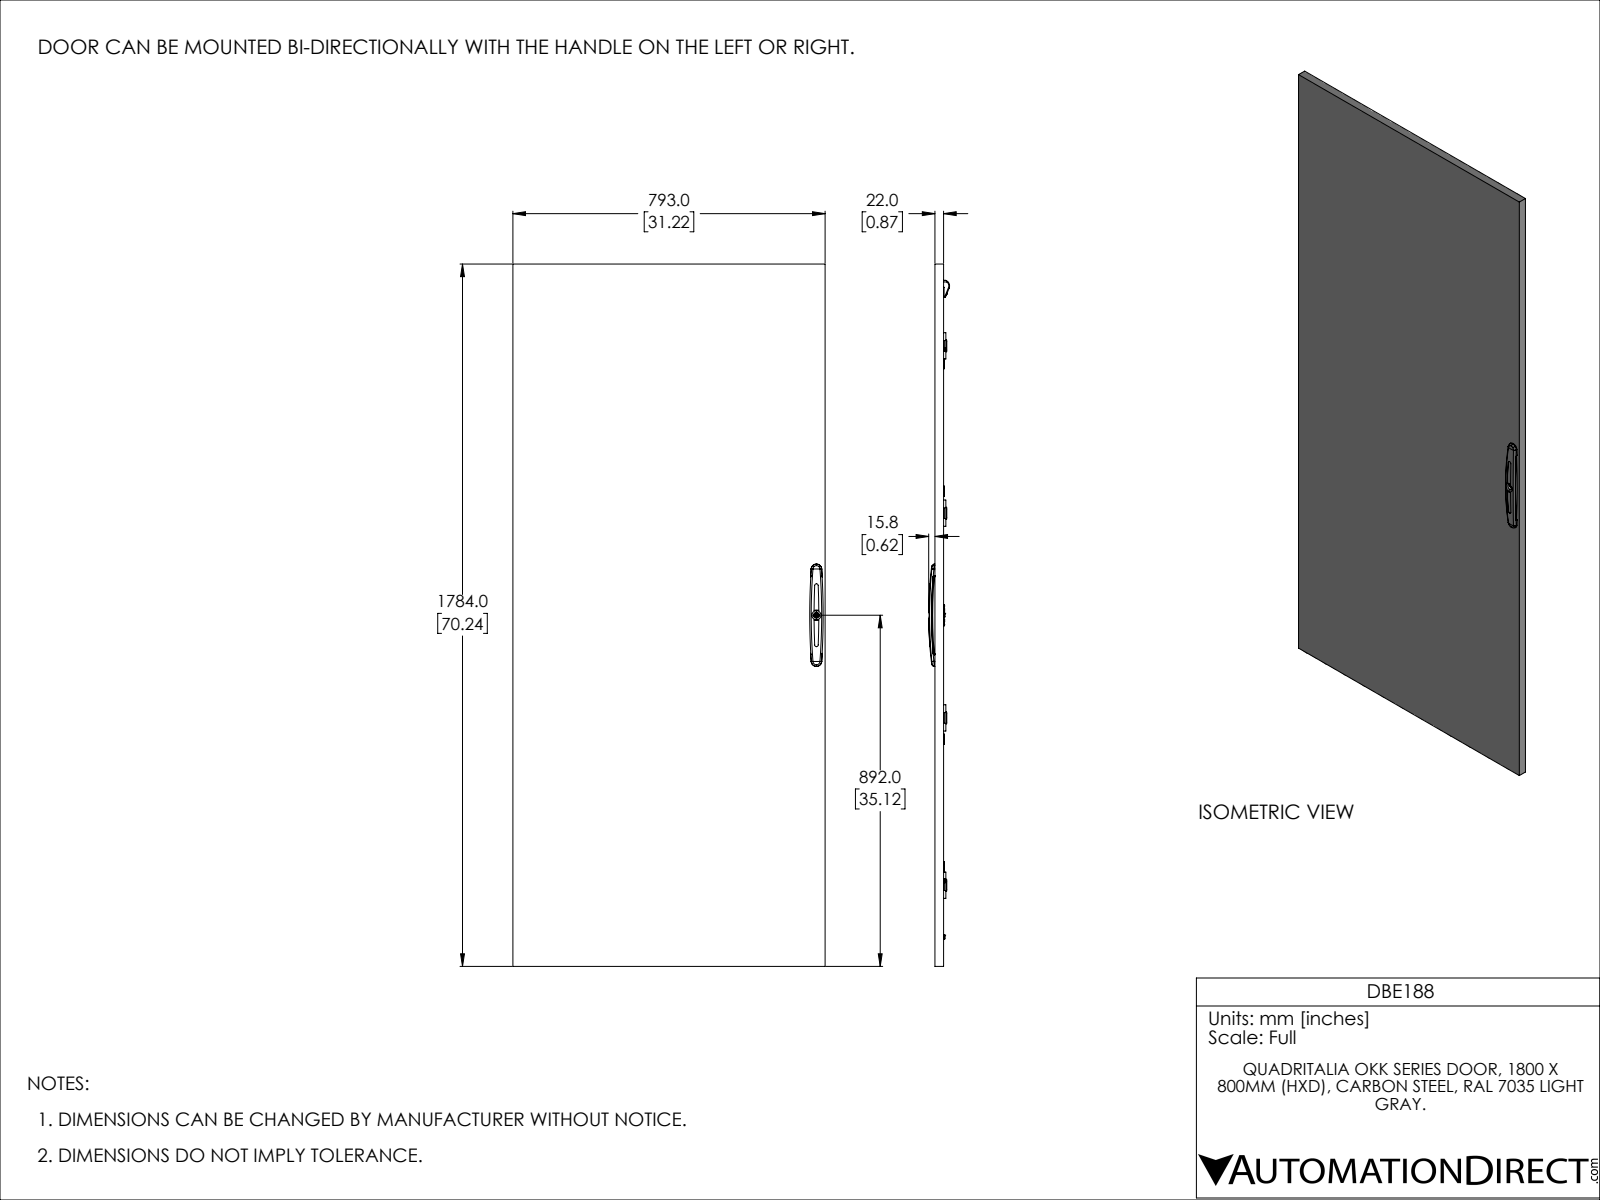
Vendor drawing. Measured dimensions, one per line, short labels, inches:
name: DBE188
written by: SolidWorks 2021 (CONFIG_CONTROL_DESIGN)
unit: in
bodies: 72 solids, 2942 faces (1431 planar, 992 cylindrical, 519 other)
size: 70.236 × 31.22 × 2.091
volume: 252.9 in³; area: 6 312 in²
holes: 136× ⌀0.167, 18× ⌀0.354, 10× ⌀0.194, 8× ⌀0.197, 3× ⌀0.205, 2× ⌀0.134, 2× ⌀0.169, 2× ⌀0.173, 2× ⌀0.177, 2× ⌀0.236, 1× ⌀0.196, 1× ⌀0.295
bosses: 18× ⌀0.276, 18× ⌀0.236, 10× ⌀0.283, 8× ⌀0.193, 2× ⌀0.472, 2× ⌀0.394, 2× ⌀0.315, 2× ⌀0.157
rounds: 74× R0.012, 70× R0.039, 35× R0.02, 28× R0.098, 19× R0.079, 16× R0.177, 10× R0.227, 8× R0.008
face distances: 0.079, 0.059, 0.728, 0.787, 0.669, 25.984, 0.866, 0.138, 0.807, 31.142
hole spacings: 0.984, 1.969, 2.953, 8.858, 3.937, 4.921, 5.906, 6.89
